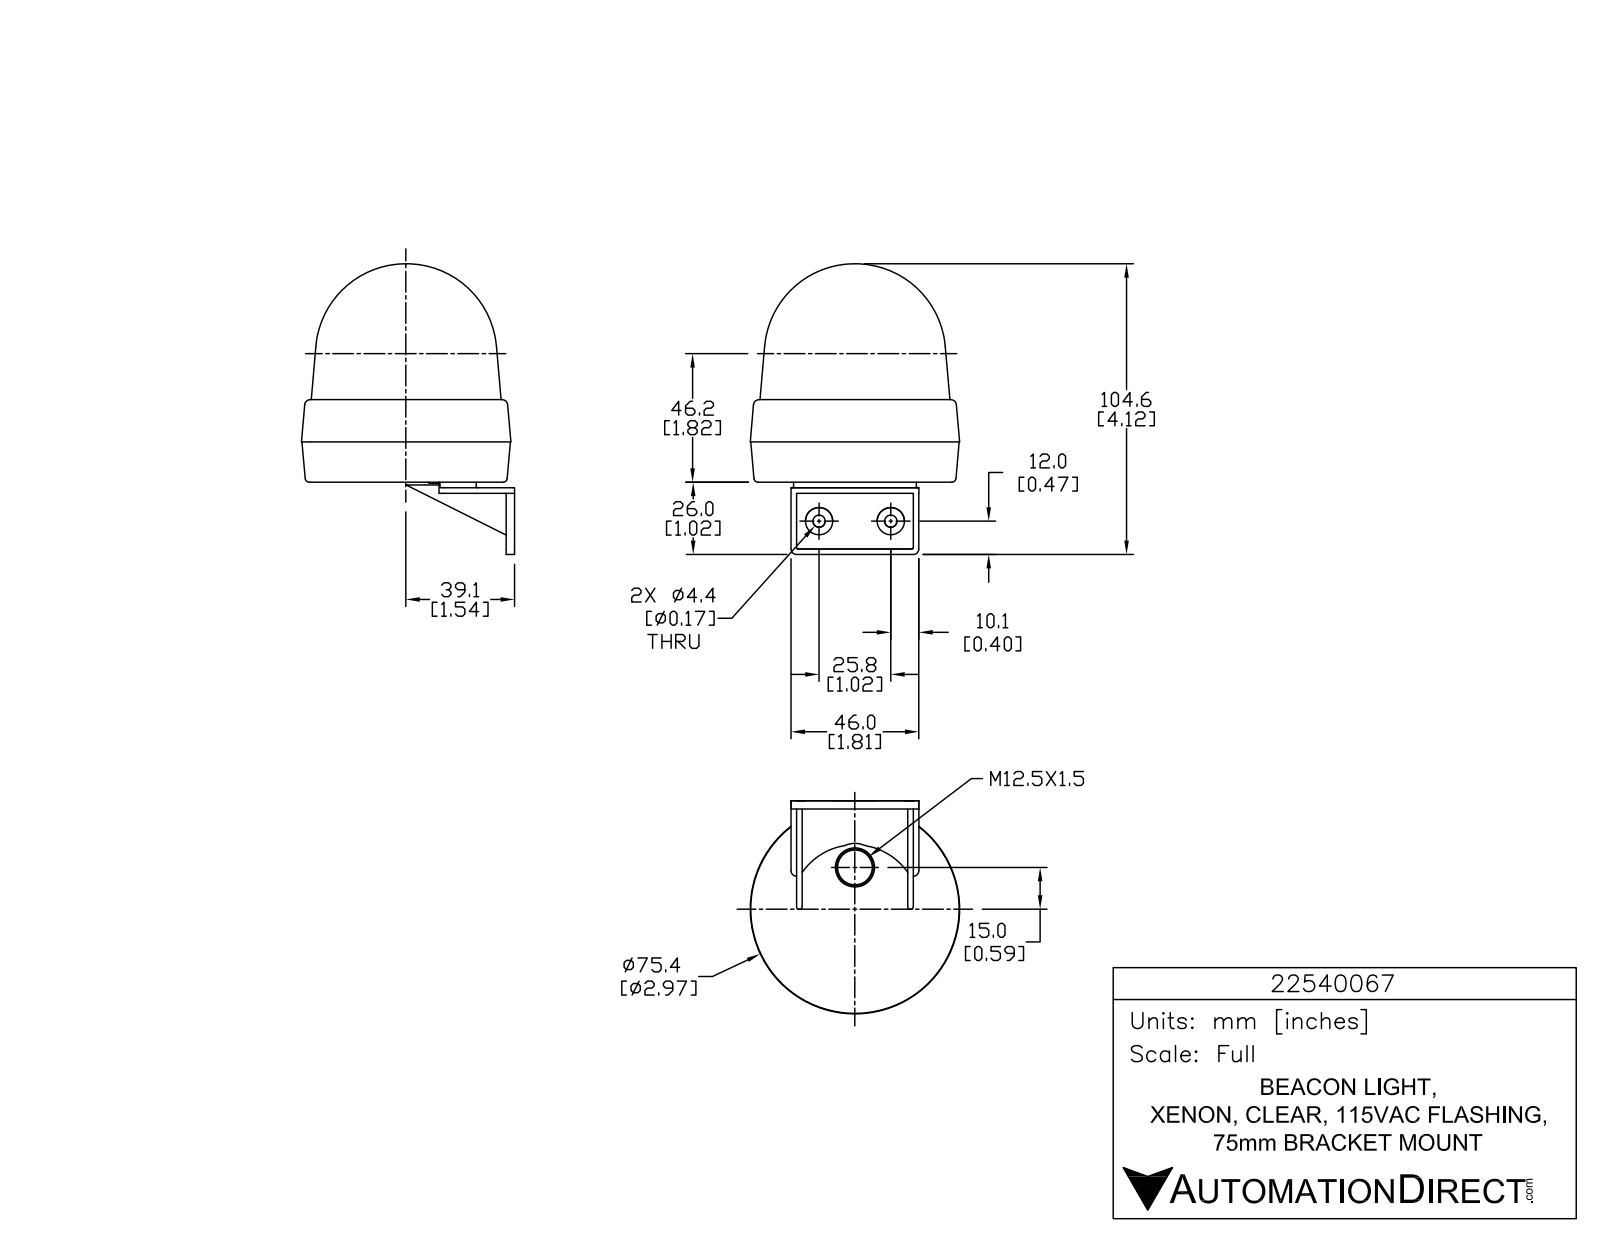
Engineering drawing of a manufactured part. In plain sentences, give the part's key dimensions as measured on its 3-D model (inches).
The part is named "22540067". Its 3-D file was written by "SolidWorks 2015 (AUTOMOTIVE_DESIGN)". It is 1 solid with 819 faces: 549 planar, 180 cylindrical and 90 other. Overall it measures 4.117 by 3.253 by 2.967 inches. Its volume is 16.02 cubic inches and its surface area 41.97 square inches. Round holes: 3 of diameter 0.059, 2 of diameter 0.173. Round bosses or shafts: 3 of diameter 0.339, 3 of diameter 0.084, 2 of diameter 0.386. Partial cylindrical surfaces (rounded edges, fillets, slot ends): 9 of radius 0.005, 6 of radius 0.005, 6 of radius 0.012, 6 of radius 0.012, 6 of radius 0.012, 6 of radius 0.02, 6 of radius 0.196, 4 of radius 0.079. The main face-to-face distances are 0.079, 0.157, 1.574, 0.039, 0.118, 1.653, 1.496, 0.079, 1.654, 1.732. The hole center spacings are 1.016.
